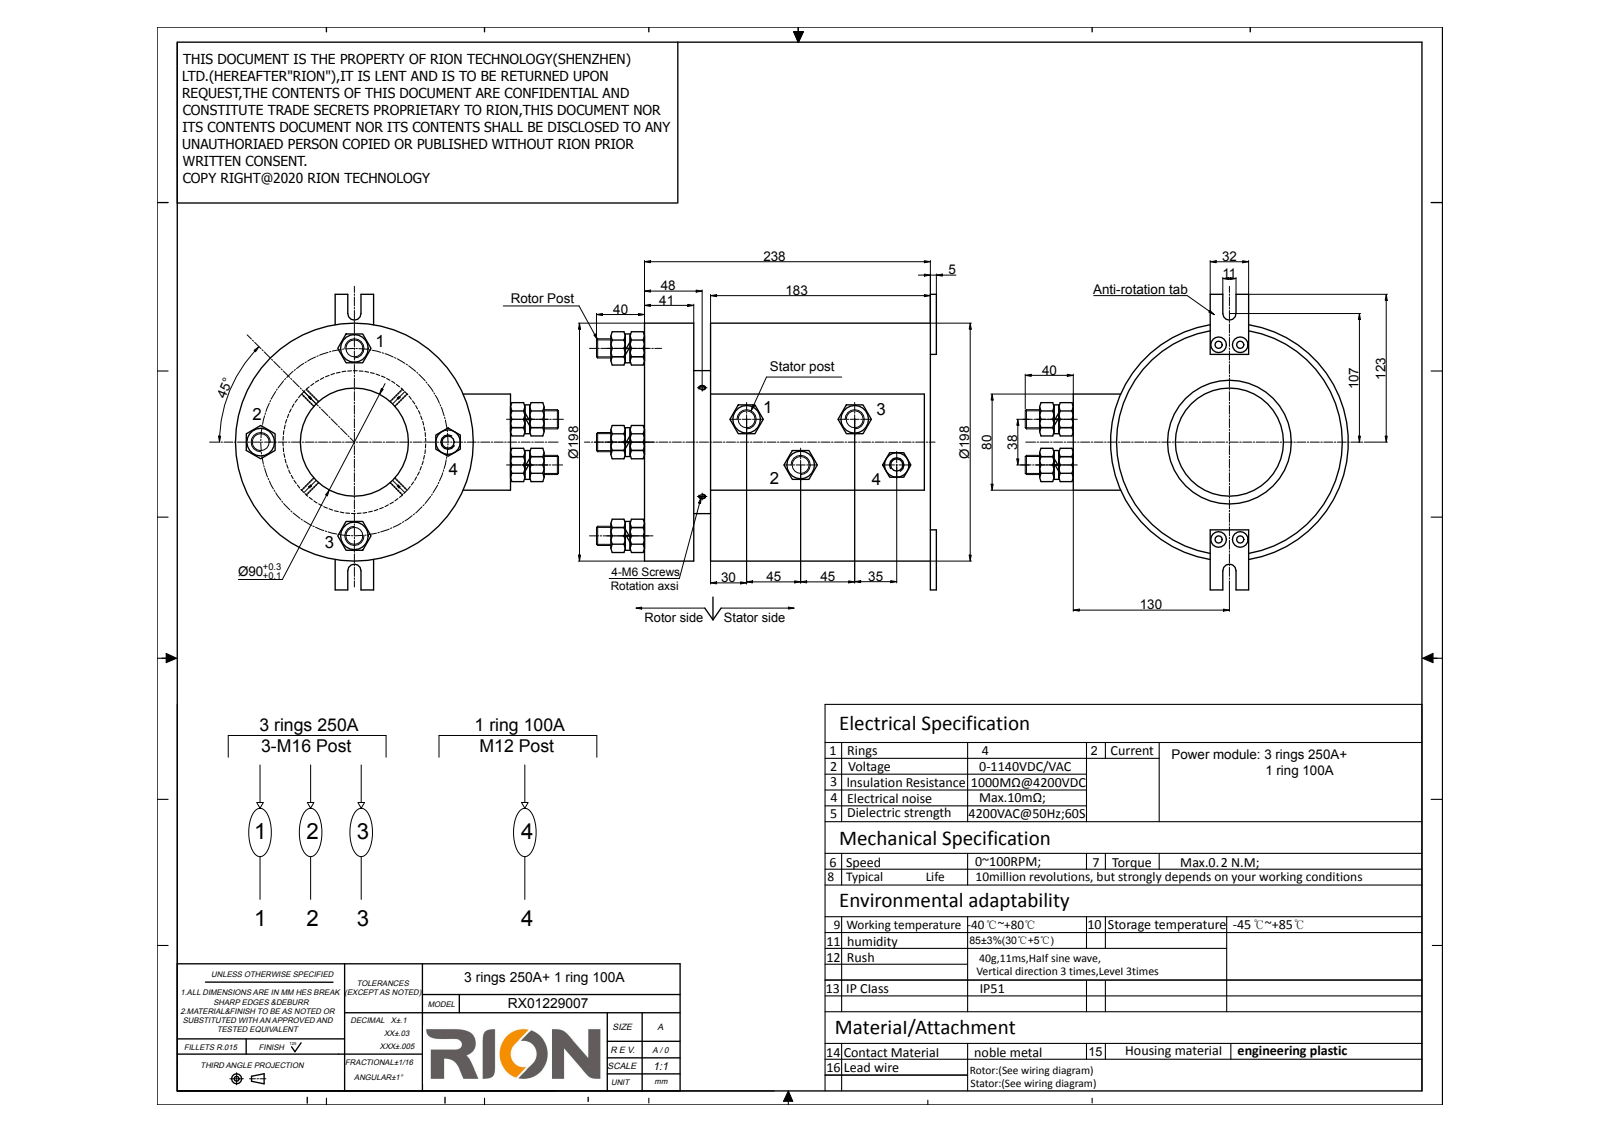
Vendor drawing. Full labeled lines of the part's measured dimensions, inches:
Part name (STEP PRODUCT): RX01229007
STEP written by: SolidWorks 2014 (CONFIG_CONTROL_DESIGN)
Units: inches
Bodies: 1 solid, 319 faces (245 planar, 66 cylindrical, 8 other)
Overall size (bounding box): 11.142 × 10.591 × 9.685
Volume: 375.9 in³ · Surface area: 541.4 in²
Round holes (diameter × count): ⌀0.197 ×4, ⌀0.236 ×4, ⌀3.543 ×1, ⌀4.071 ×1, ⌀7.417 ×1
Round bosses / shafts (diameter × count): ⌀0.945 ×8, ⌀0.63 ×8, ⌀7.795 ×1, ⌀7.402 ×1, ⌀4.685 ×1, ⌀4.055 ×1
Partial cylindrical surfaces — rounded edges, fillets, slot ends (radius × count): R0.217 ×2
Main face-to-face distances: 9.37, 2.165, 7.205, 0.551, 1.614, 7.756, 0.945, 3.15, 0.197, 1.102
Hole centre spacings: 3.209, 0.709, 6.378, 6.417
